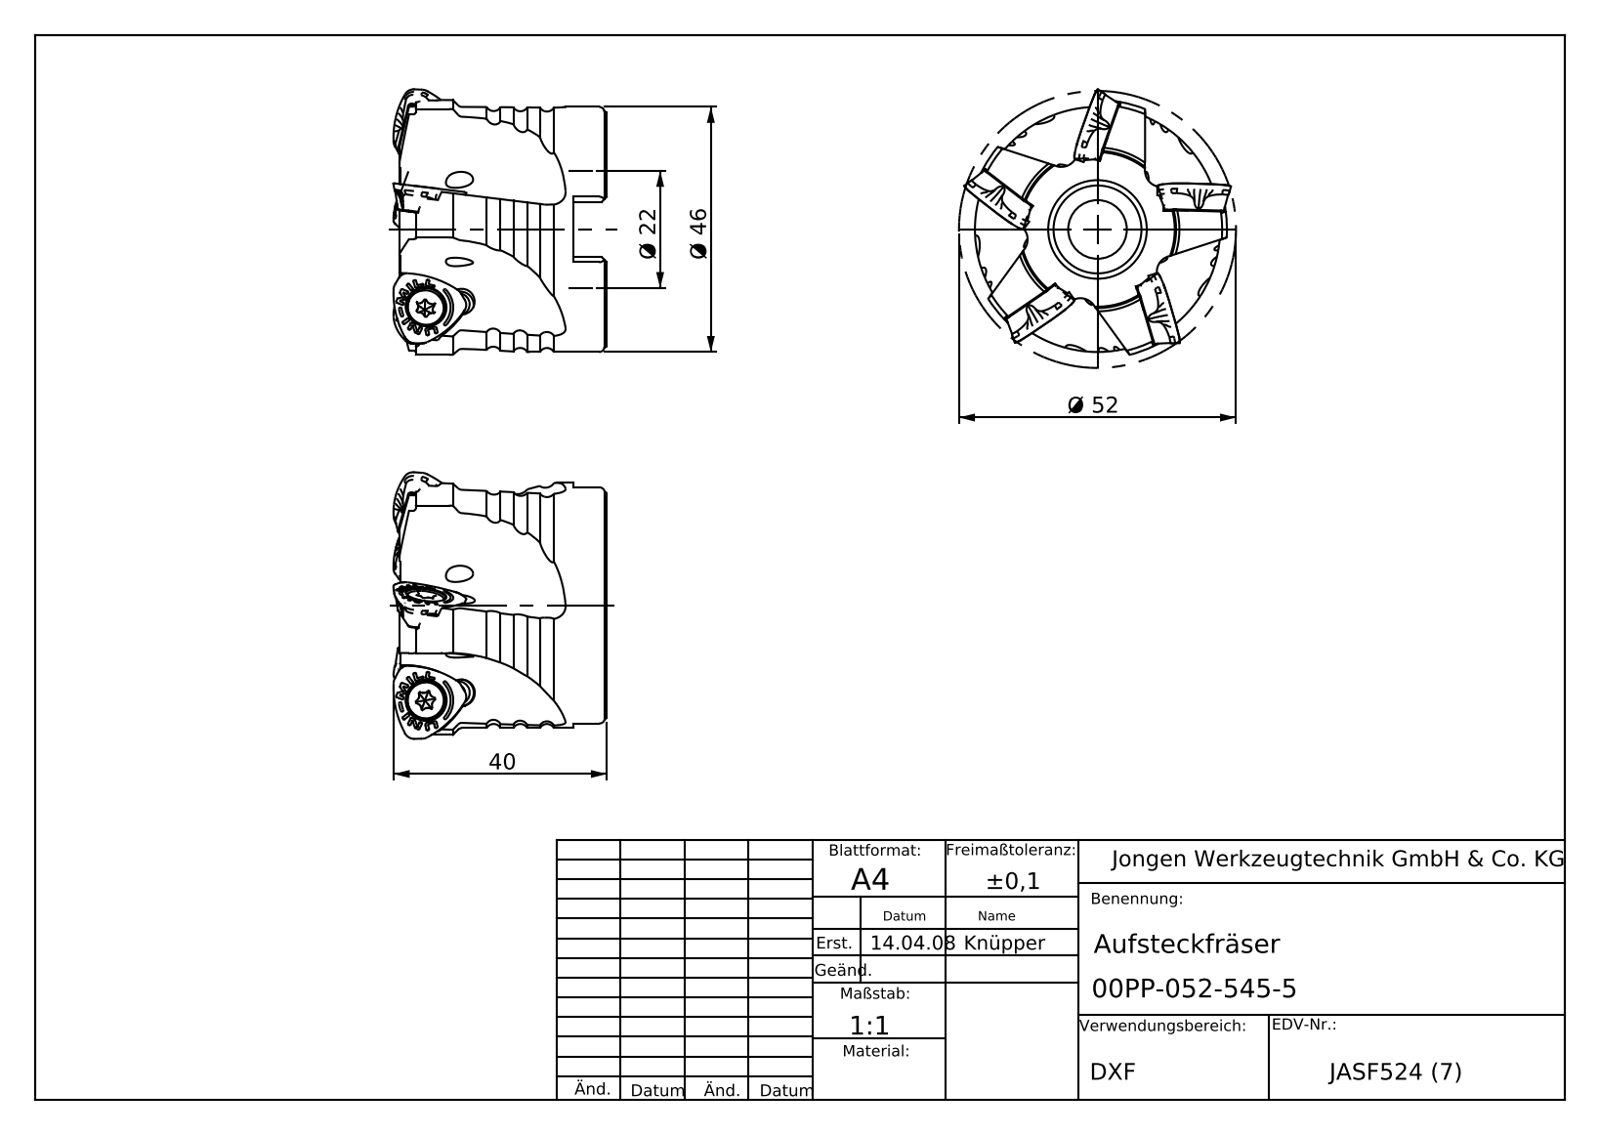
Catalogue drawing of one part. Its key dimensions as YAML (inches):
part_name: "00PP-052-545-5"
step_written_by: "SolidWorks 2012 (AUTOMOTIVE_DESIGN)"
units: inches
bodies: {solids: 1, faces: 286, planar: 98, cylindrical: 86, other: 102}
overall_size: [2.048, 2.047, 1.577]
volume: 2.816
surface_area: 21.53
round_holes:
  - {diameter: 0.118, count: 5}
  - {diameter: 0.433, count: 1}
  - {diameter: 0.65, count: 1}
  - {diameter: 0.866, count: 1}
  - {diameter: 0.872, count: 1}
  - {diameter: 0.878, count: 1}
round_bosses_or_shafts:
  - {diameter: 1.811, count: 1}
partial_cylinders:
  - {radius: 0.059, count: 10}
  - {radius: 0.098, count: 5}
  - {radius: 0.118, count: 5}
  - {radius: 1.102, count: 5}
  - {radius: 0.957, count: 1}
face_to_face_distances: [1.522, 0.246, 1.276, 0.409, 1.1, 0.854, 0.421, 0.063, 0.063, 0.787]
